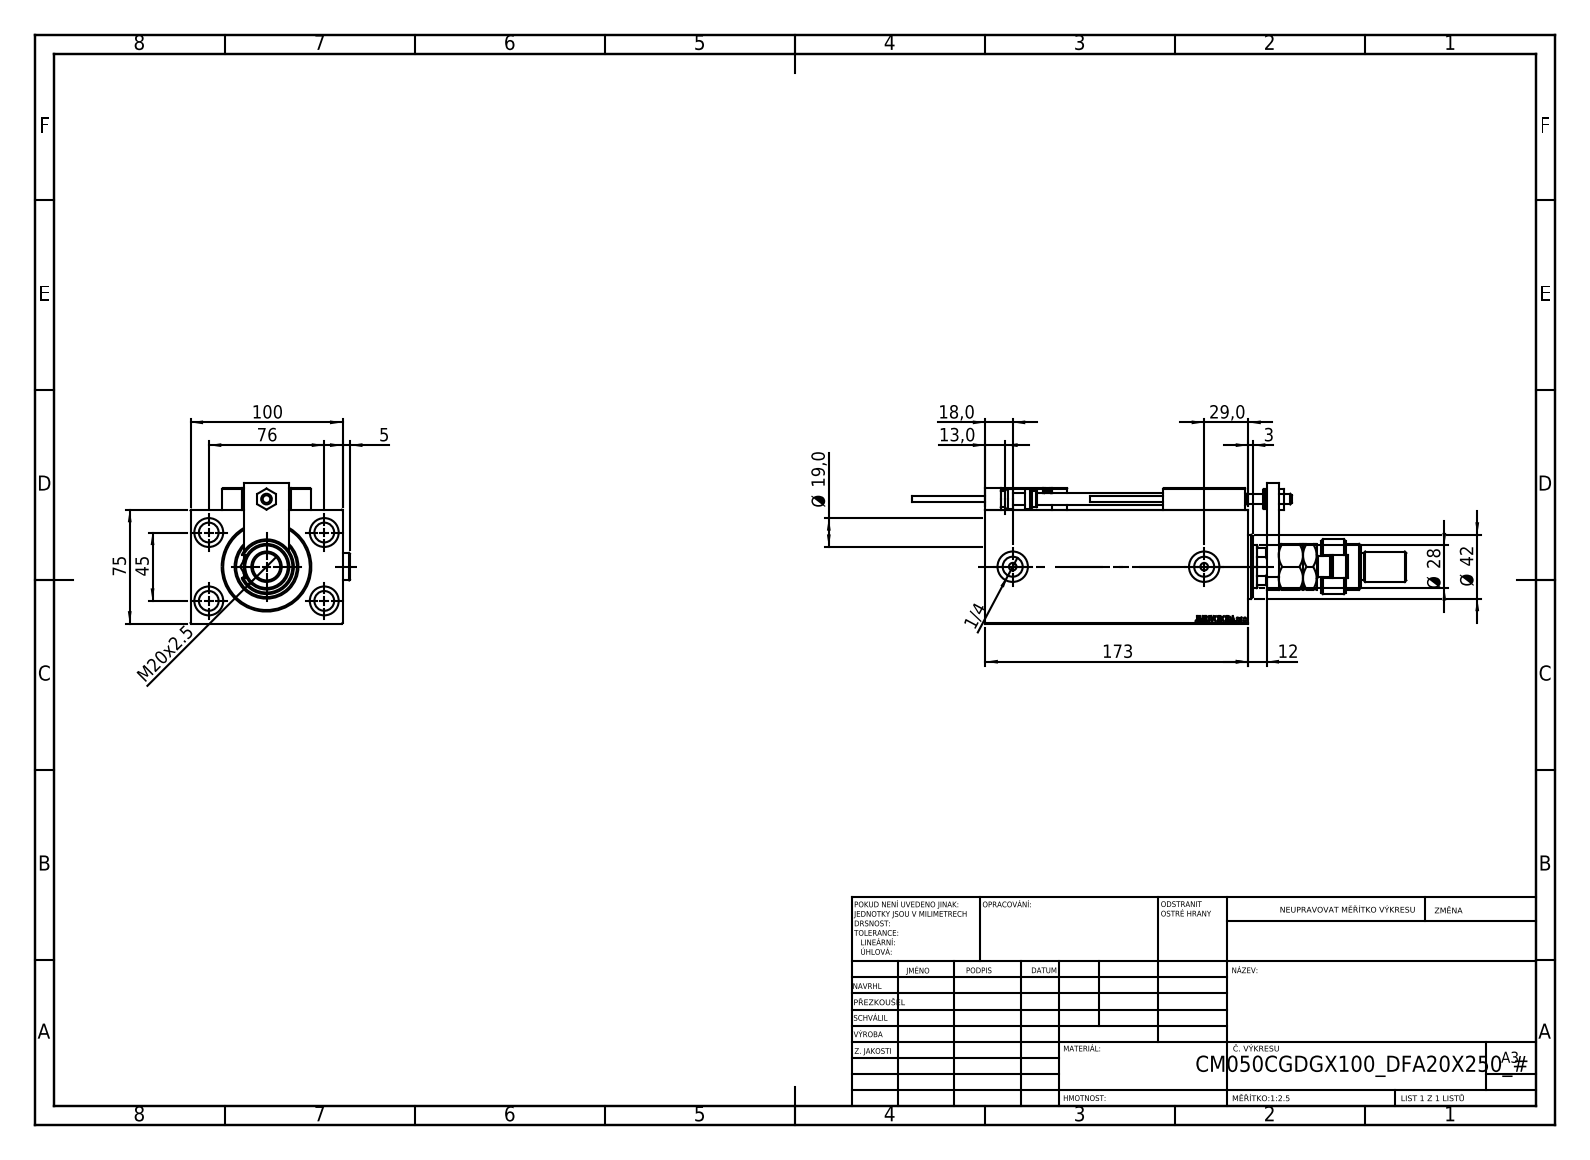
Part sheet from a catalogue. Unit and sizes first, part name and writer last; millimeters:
Units: millimetres
Overall size (bounding box): 325 × 104.9 × 92.5
Round holes (diameter × count): ⌀8 ×5, ⌀3.2 ×4, ⌀4 ×4, ⌀5 ×4, ⌀13 ×4, ⌀19 ×4, ⌀20 ×3, ⌀13.16 ×2, ⌀7 ×1, ⌀18.5 ×1, ⌀28 ×1, ⌀31.5 ×1
Round bosses / shafts (diameter × count): ⌀18 ×3, ⌀5 ×2, ⌀3.8 ×2, ⌀42 ×1, ⌀36 ×1, ⌀30 ×1, ⌀22 ×1, ⌀14 ×1
Partial cylindrical surfaces — rounded edges, fillets, slot ends (radius × count): R0.3 ×30, R3 ×2, R7.5 ×1, R12 ×1, R13.5 ×1
Main face-to-face distances: 75, 100, 14, 173, 12, 159, 20, 8, 24, 25
Hole centre spacings: 44.16, 11.37, 20, 29.59, 29.69, 36.06, 42.19, 43.91
Volume: 1 159 000 mm³ · Surface area: 207 150 mm²
Bodies: 27 solids, 1424 faces (623 planar, 219 cylindrical, 582 other)
Part name (STEP PRODUCT): ALLEN BOLT D5; SWITCH X; MFA; V450CM_C_Body (+7 more)
STEP written by: SolidWorks 2019 (CONFIG_CONTROL_DESIGN)
